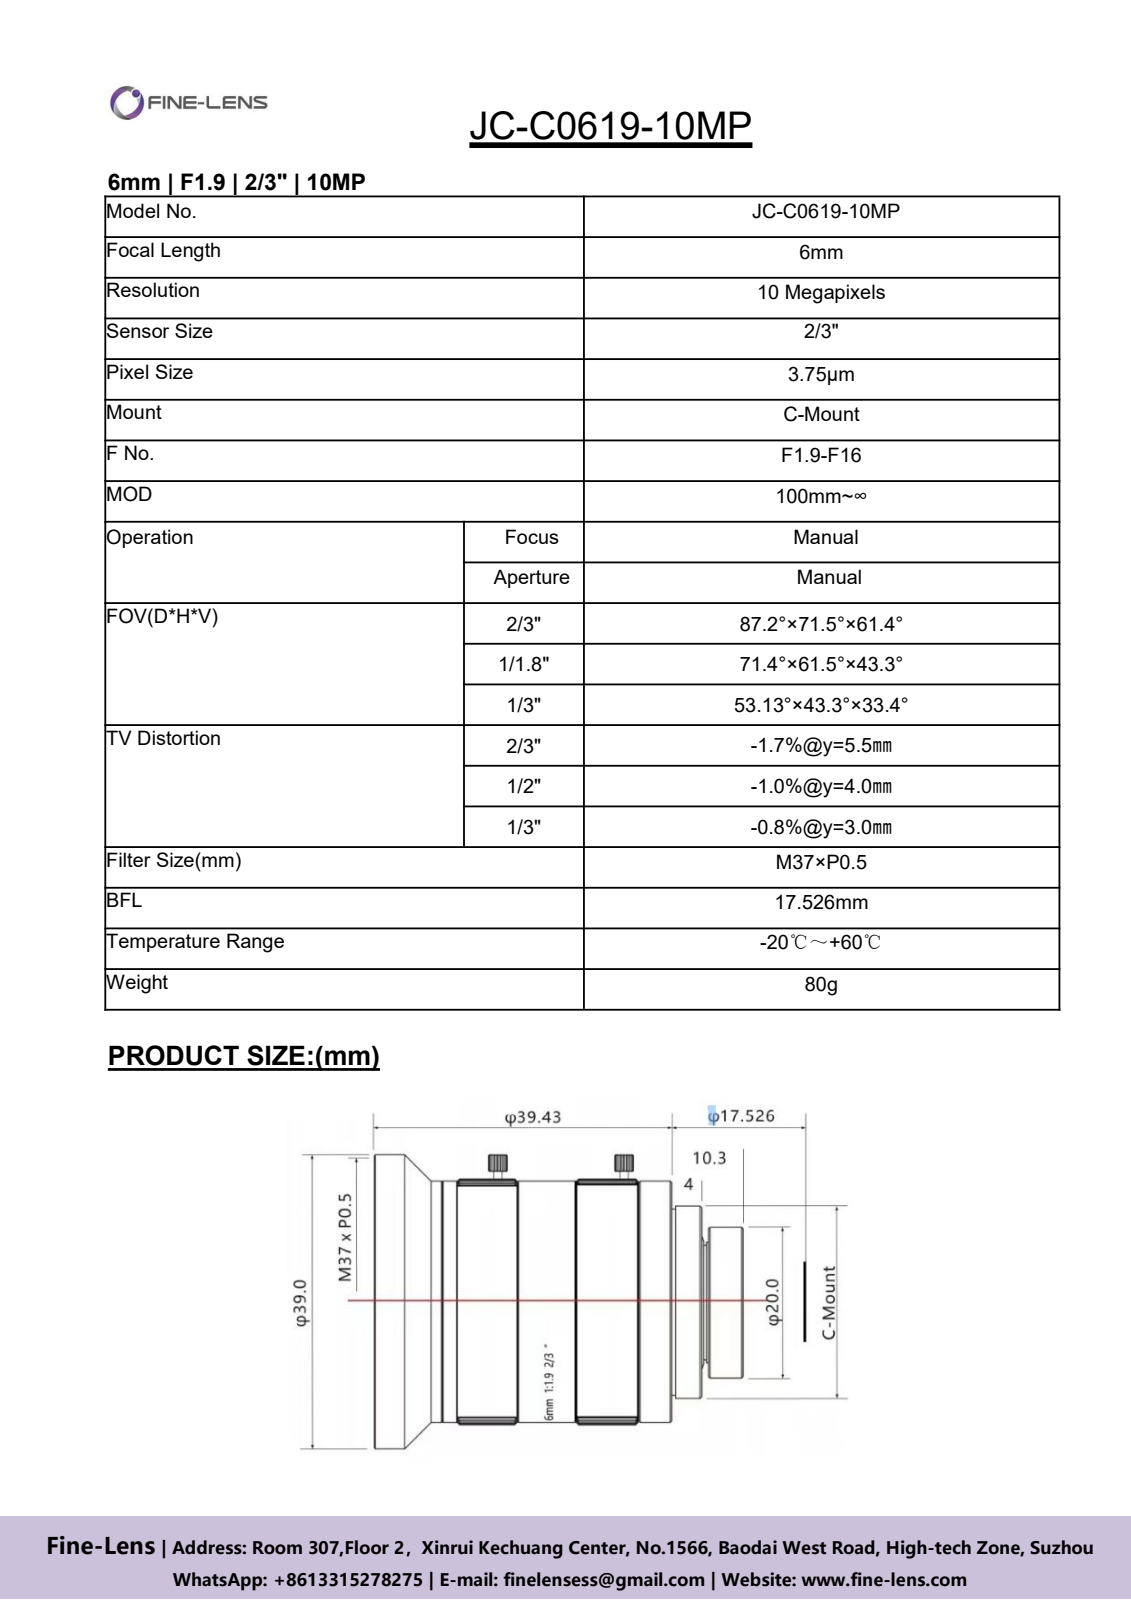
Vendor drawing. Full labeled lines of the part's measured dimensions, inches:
Part name (STEP PRODUCT): FM3007-3D
STEP written by: CREO PARAMETRIC BY PTC INC, 2018100 (CONFIG_CONTROL_DESIGN)
Units: inches
Bodies: 1 solid, 1861 faces (602 planar, 416 cylindrical, 843 other)
Overall size (bounding box): 1.917 × 1.535 × 1.535
Volume: 1.545 in³ · Surface area: 31.24 in²
Round holes (diameter × count): ⌀0.059 ×13, ⌀0.098 ×8, ⌀0.039 ×7, ⌀0.067 ×4, ⌀0.047 ×3, ⌀0.079 ×3, ⌀0.051 ×2, ⌀0.307 ×1, ⌀0.354 ×1, ⌀0.364 ×1, ⌀0.374 ×1, ⌀0.386 ×1
Round bosses / shafts (diameter × count): ⌀1.535 ×1, ⌀1.26 ×1, ⌀1.213 ×1, ⌀1.189 ×1, ⌀1.169 ×1, ⌀1.091 ×1, ⌀1.071 ×1, ⌀1.051 ×1
Partial cylindrical surfaces — rounded edges, fillets, slot ends (radius × count): R0.049 ×12, R0.039 ×6, R0.03 ×2, R0.291 ×1, R0.295 ×1, R0.627 ×1, R0.628 ×1, R0.642 ×1
Main face-to-face distances: 1.363, 0.157, 1.374, 0.039, 1.173, 0.169, 1.206, 0.652, 1.739, 1.728
Hole centre spacings: 0.334, 0.336, 0.047, 0.118, 0.12, 0.214, 0.216, 0.234
